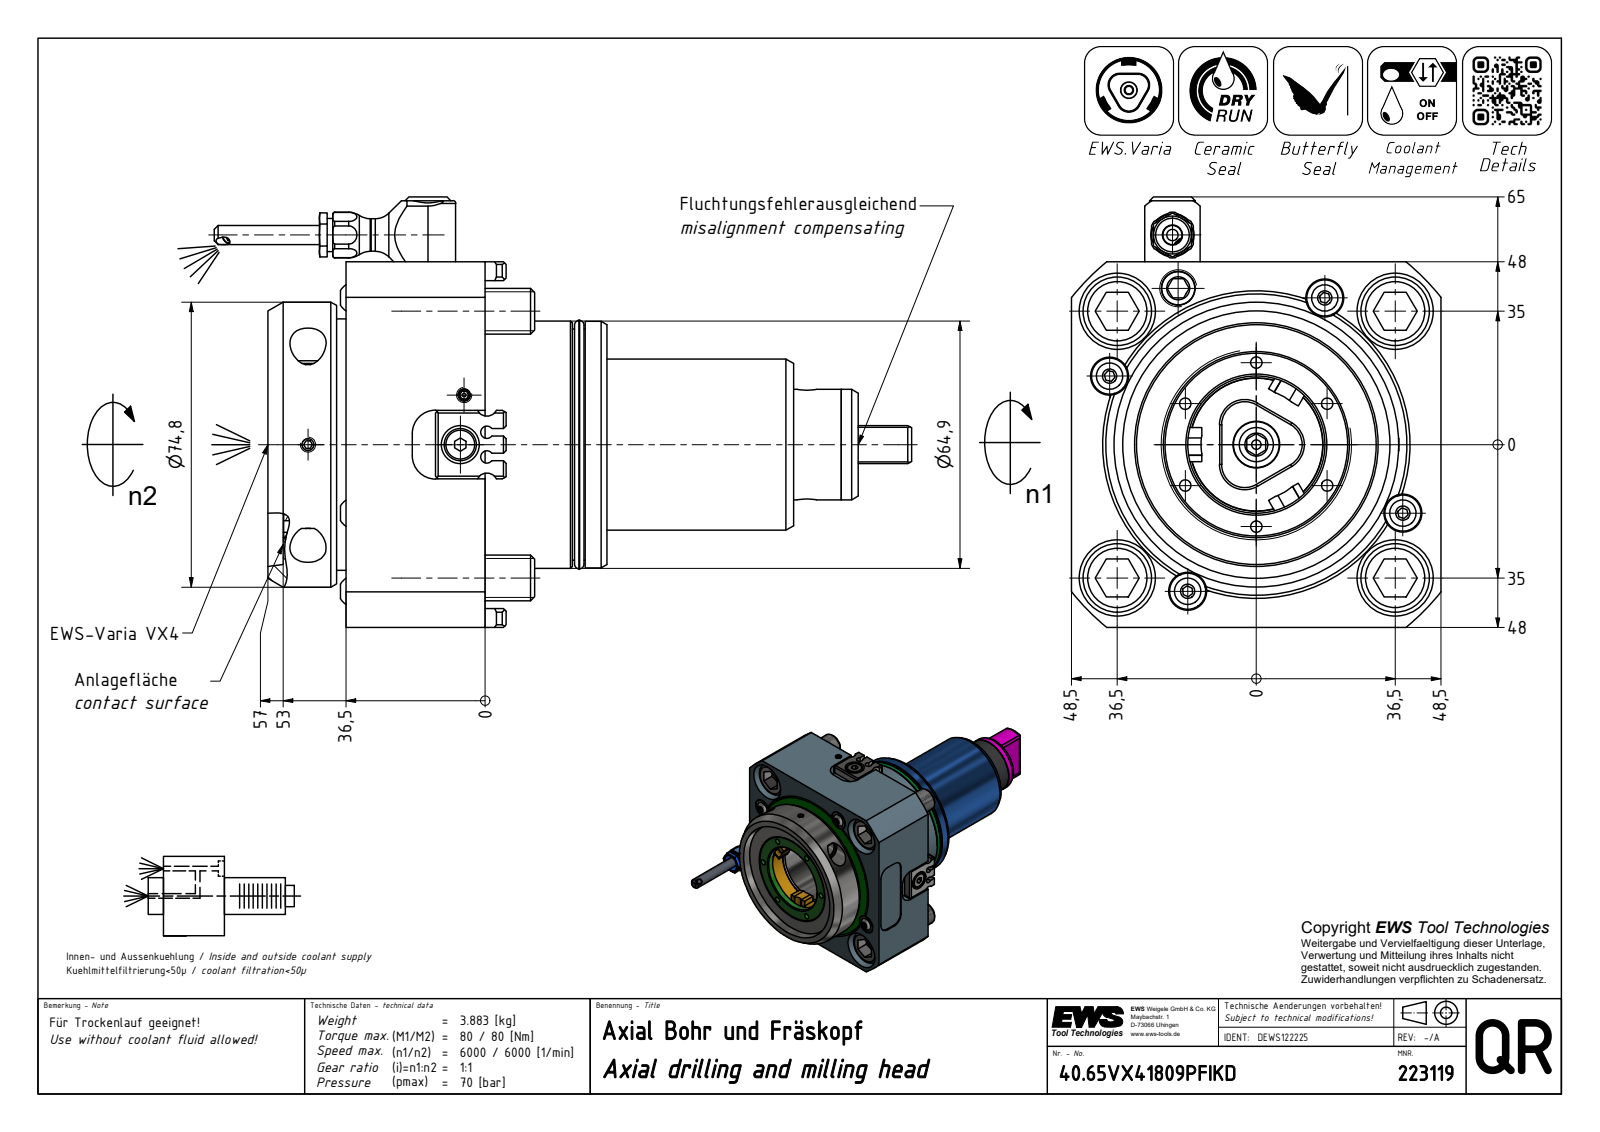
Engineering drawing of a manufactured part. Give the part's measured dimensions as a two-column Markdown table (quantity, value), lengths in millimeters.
| quantity | value |
| --- | --- |
| part name | EWS_223119_DIN4003 |
| STEP written by | HOOPS Exchange (AUTOMOTIVE_DESIGN) |
| units | millimeters |
| bodies | 1 solid, 304 faces (167 planar, 74 cylindrical, 63 other) |
| overall size | 183.1 × 113 × 97 |
| volume | 620 457 mm³ |
| surface area | 57 604 mm² |
| round bosses / shafts (diameter × count) | 12 × 5, 74.8 × 1, 73.07 × 1, 65.39 × 1, 64.9 × 1, 64.7 × 1, 44.95 × 1, 29 × 1 |
| partial cylindrical surfaces (radius × count) | 1.65 × 4, 2.75 × 4, 6 × 1, 7.25 × 1, 10.5 × 1, 13.5 × 1, 62 × 1 |
| main face-to-face distances | 36.5, 53, 16.5, 97, 96, 85, 32, 68.5, 49, 134 |
